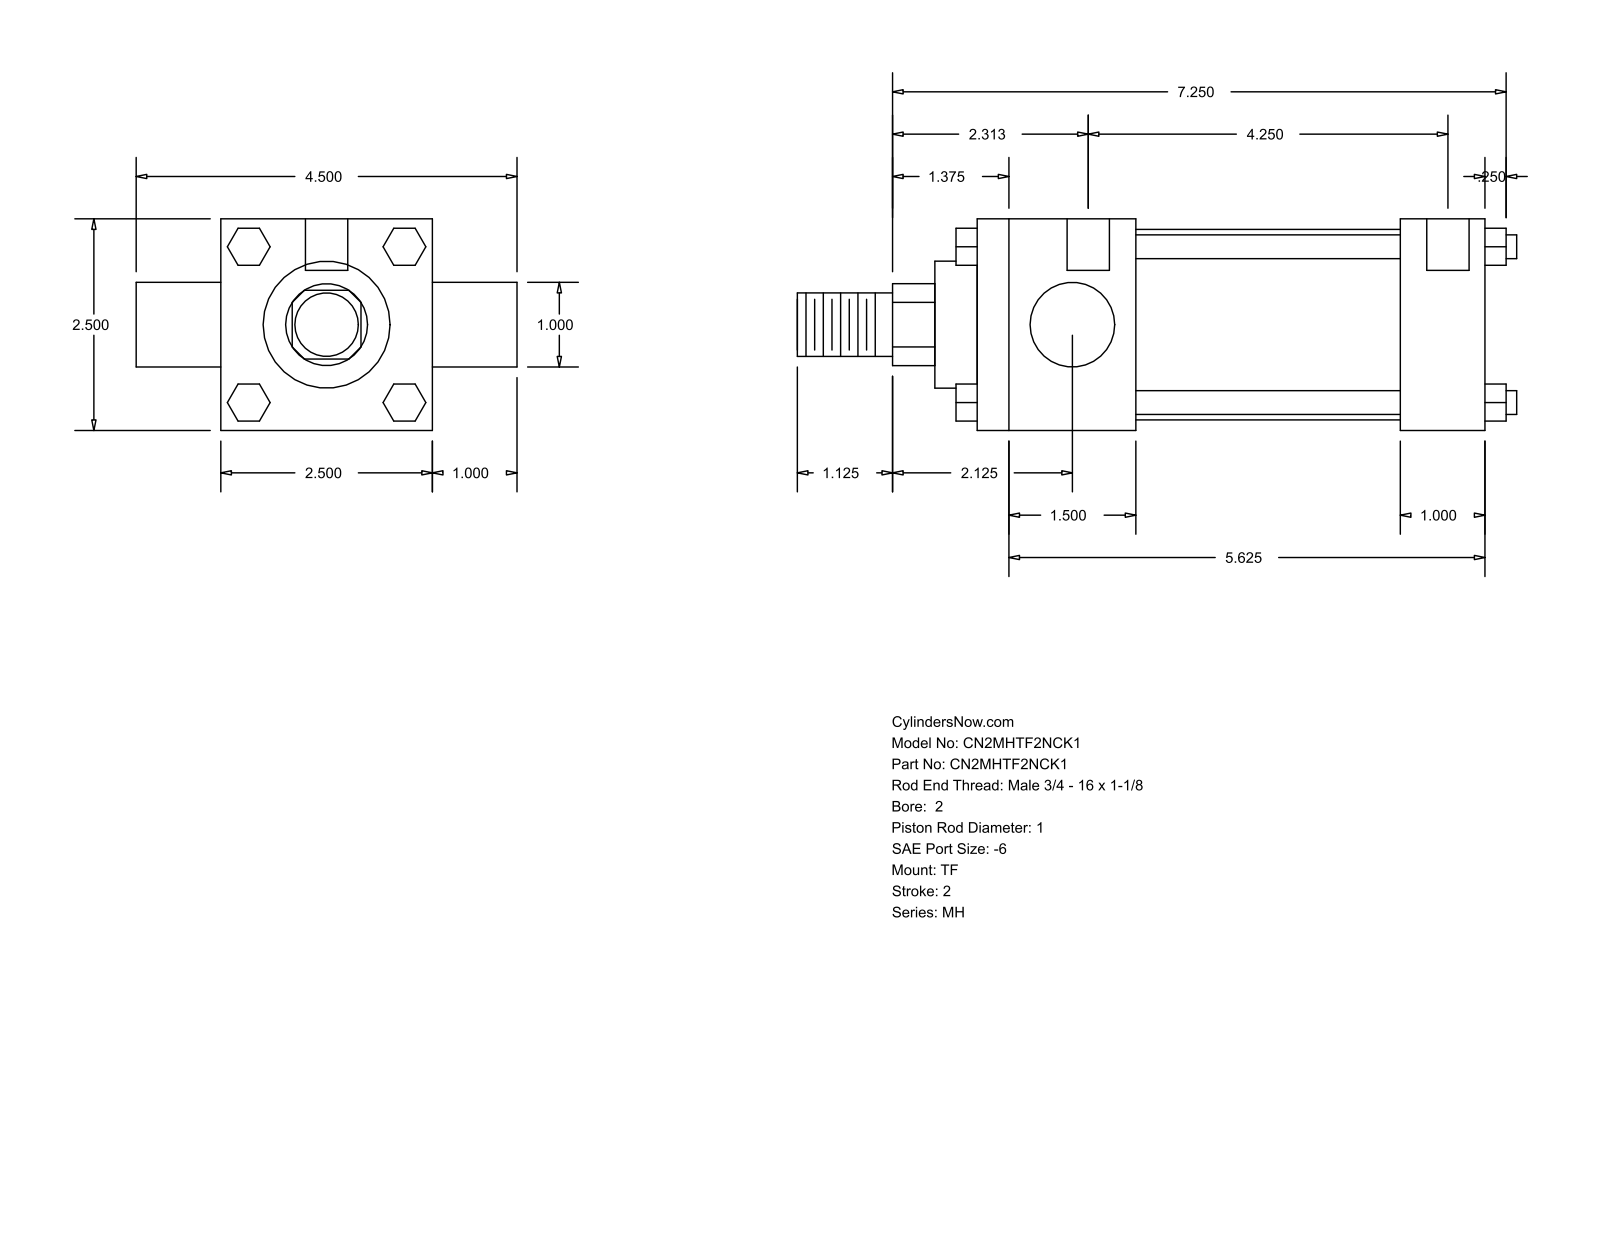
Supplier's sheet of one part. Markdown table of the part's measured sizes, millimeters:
| quantity | value |
| --- | --- |
| part name | MH_TF__0200_1 |
| STEP written by | GSSL Pune (CONFIG_CONTROL_DESIGN) |
| units | millimeters |
| bodies | 0 solids, 120 faces (92 planar, 28 cylindrical, 0 other) |
| overall size | 215.9 × 114.3 × 63.5 |
| round holes (diameter × count) | 5.56 × 3, 12.7 × 2 |
| round bosses / shafts (diameter × count) | 7.14 × 4, 25.4 × 2, 57.15 × 1, 38.1 × 1, 19.05 × 1 |
| partial cylindrical surfaces (radius × count) | 12.29 × 1 |
| main face-to-face distances | 63.5, 152.4, 25.4, 47.63, 127, 79.37, 104.77, 88.9, 165.1, 6.35 |
| hole center spacings | 3.17, 4.76, 107.95, 111.12, 112.71, 115.88 |
